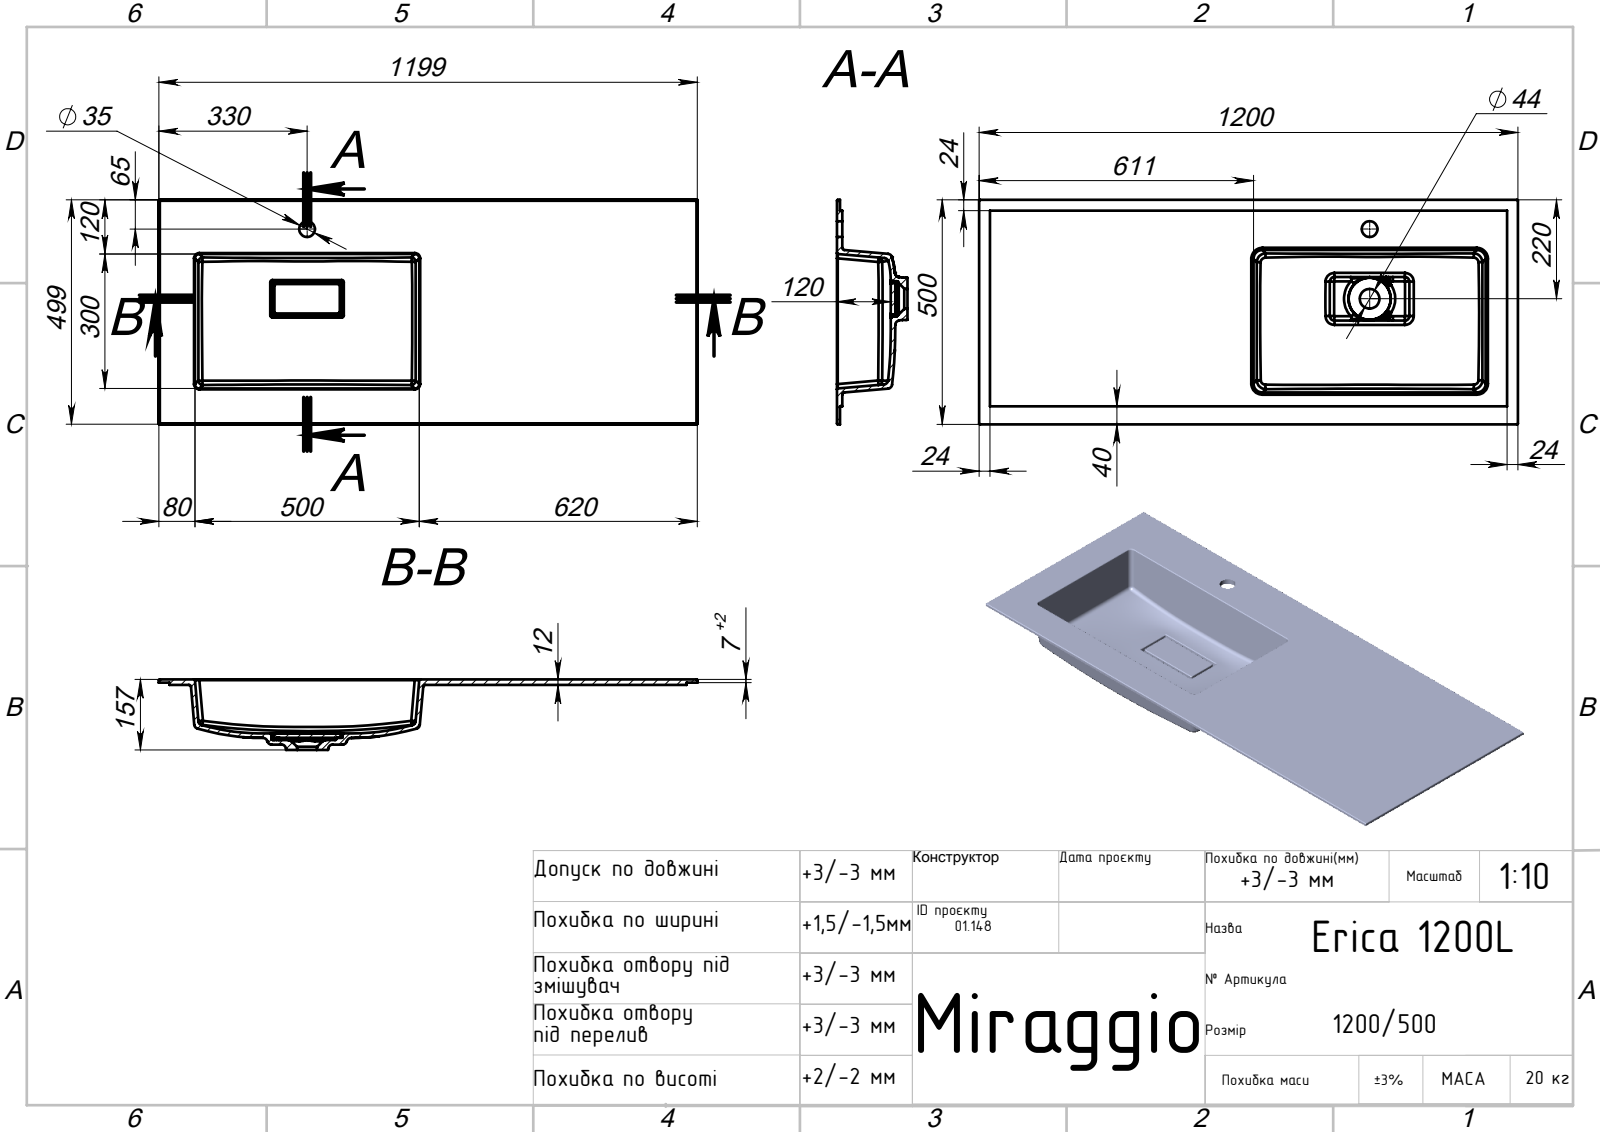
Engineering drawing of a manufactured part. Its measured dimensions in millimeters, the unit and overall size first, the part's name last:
Units: millimetres
Overall size (bounding box): 1200 × 500 × 157
Round holes (diameter × count): ⌀35 ×1
Partial cylindrical surfaces — rounded edges, fillets, slot ends (radius × count): R2 ×26, R3 ×18, R6 ×6, R5 ×4, R10 ×4, R20 ×4
Main face-to-face distances: 12, 5, 10, 7, 9.99, 123, 118, 130, 108, 113
Volume: 8 197 000 mm³ · Surface area: 1 562 000 mm²
Bodies: 2 solids, 244 faces (44 planar, 69 cylindrical, 131 other)
Part name (STEP PRODUCT): Erica 1200L
STEP written by: SolidWorks 2020 (AUTOMOTIVE_DESIGN)
